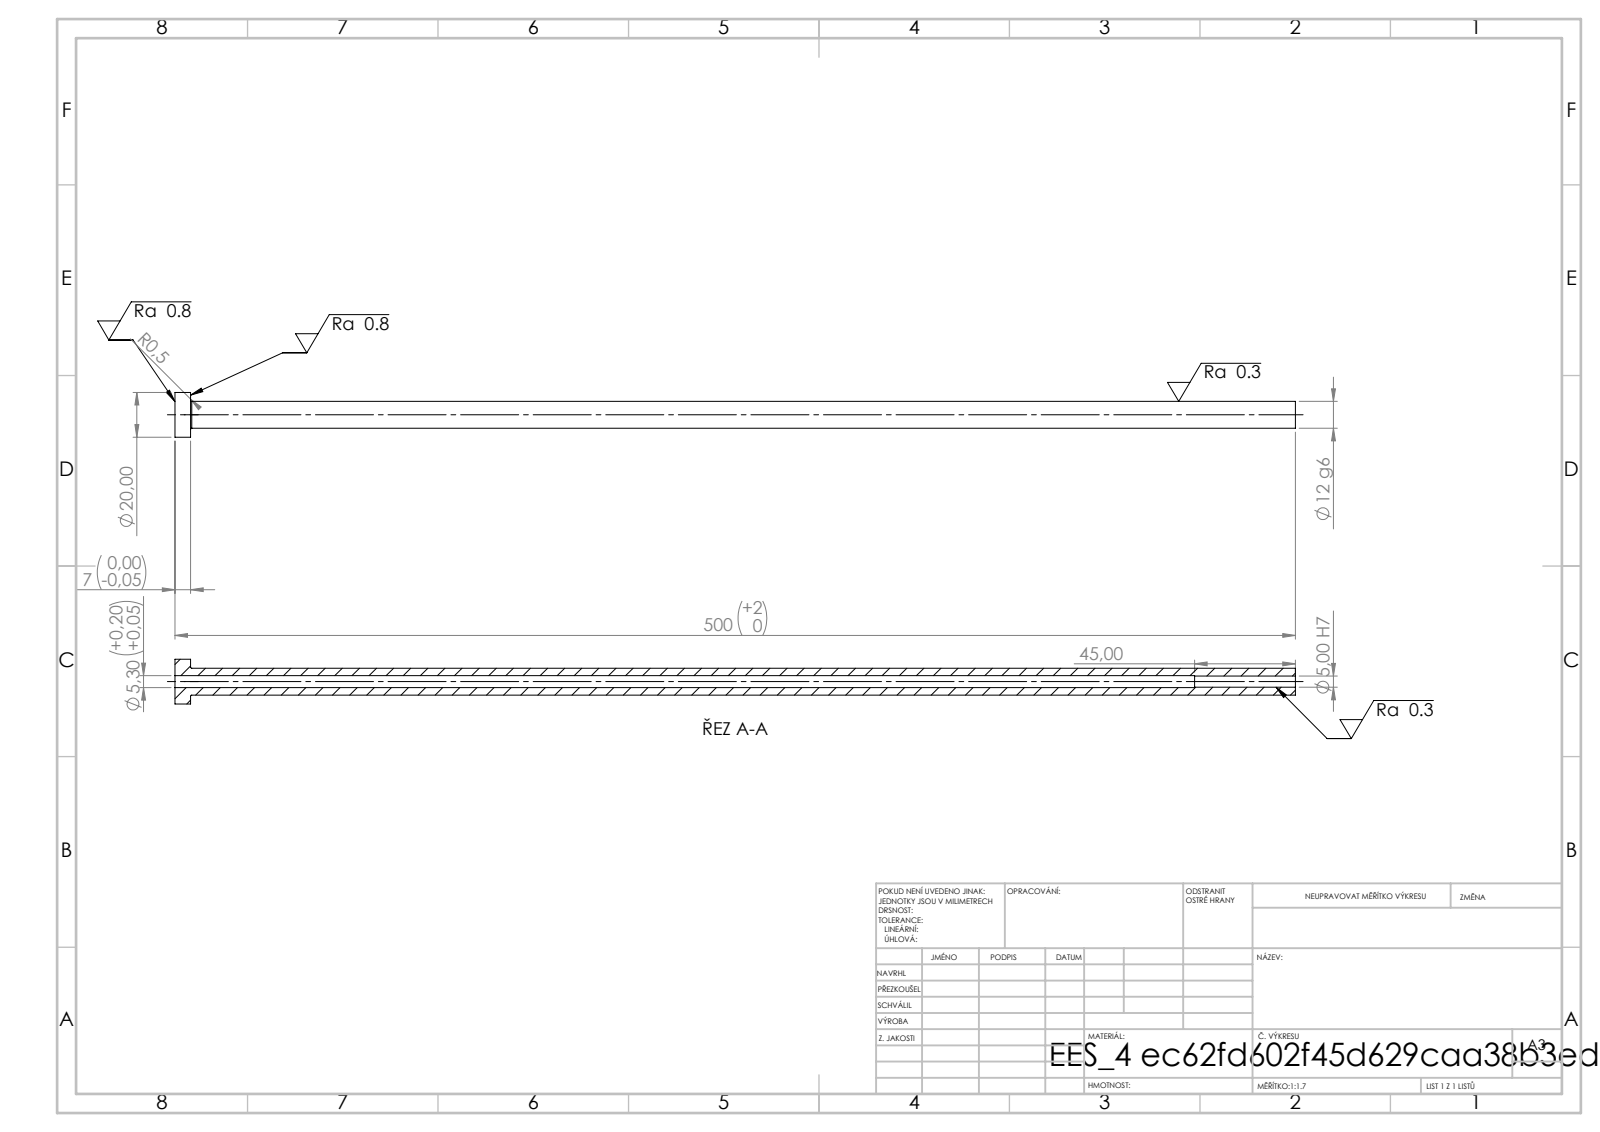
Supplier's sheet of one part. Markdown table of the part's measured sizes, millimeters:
| quantity | value |
| --- | --- |
| STEP written by | SolidWorks 2019 (CONFIG_CONTROL_DESIGN) |
| units | millimeters |
| bodies | 1 solid, 14 faces (4 planar, 8 cylindrical, 2 other) |
| overall size | 500 × 20 × 20 |
| volume | 47 036 mm³ |
| surface area | 27 889 mm² |
| round holes (diameter × count) | 5 × 1, 5.3 × 1 |
| round bosses / shafts (diameter × count) | 20 × 1, 12 × 1 |
| main face-to-face distances | 7, 500, 493, 455, 448, 45 |
